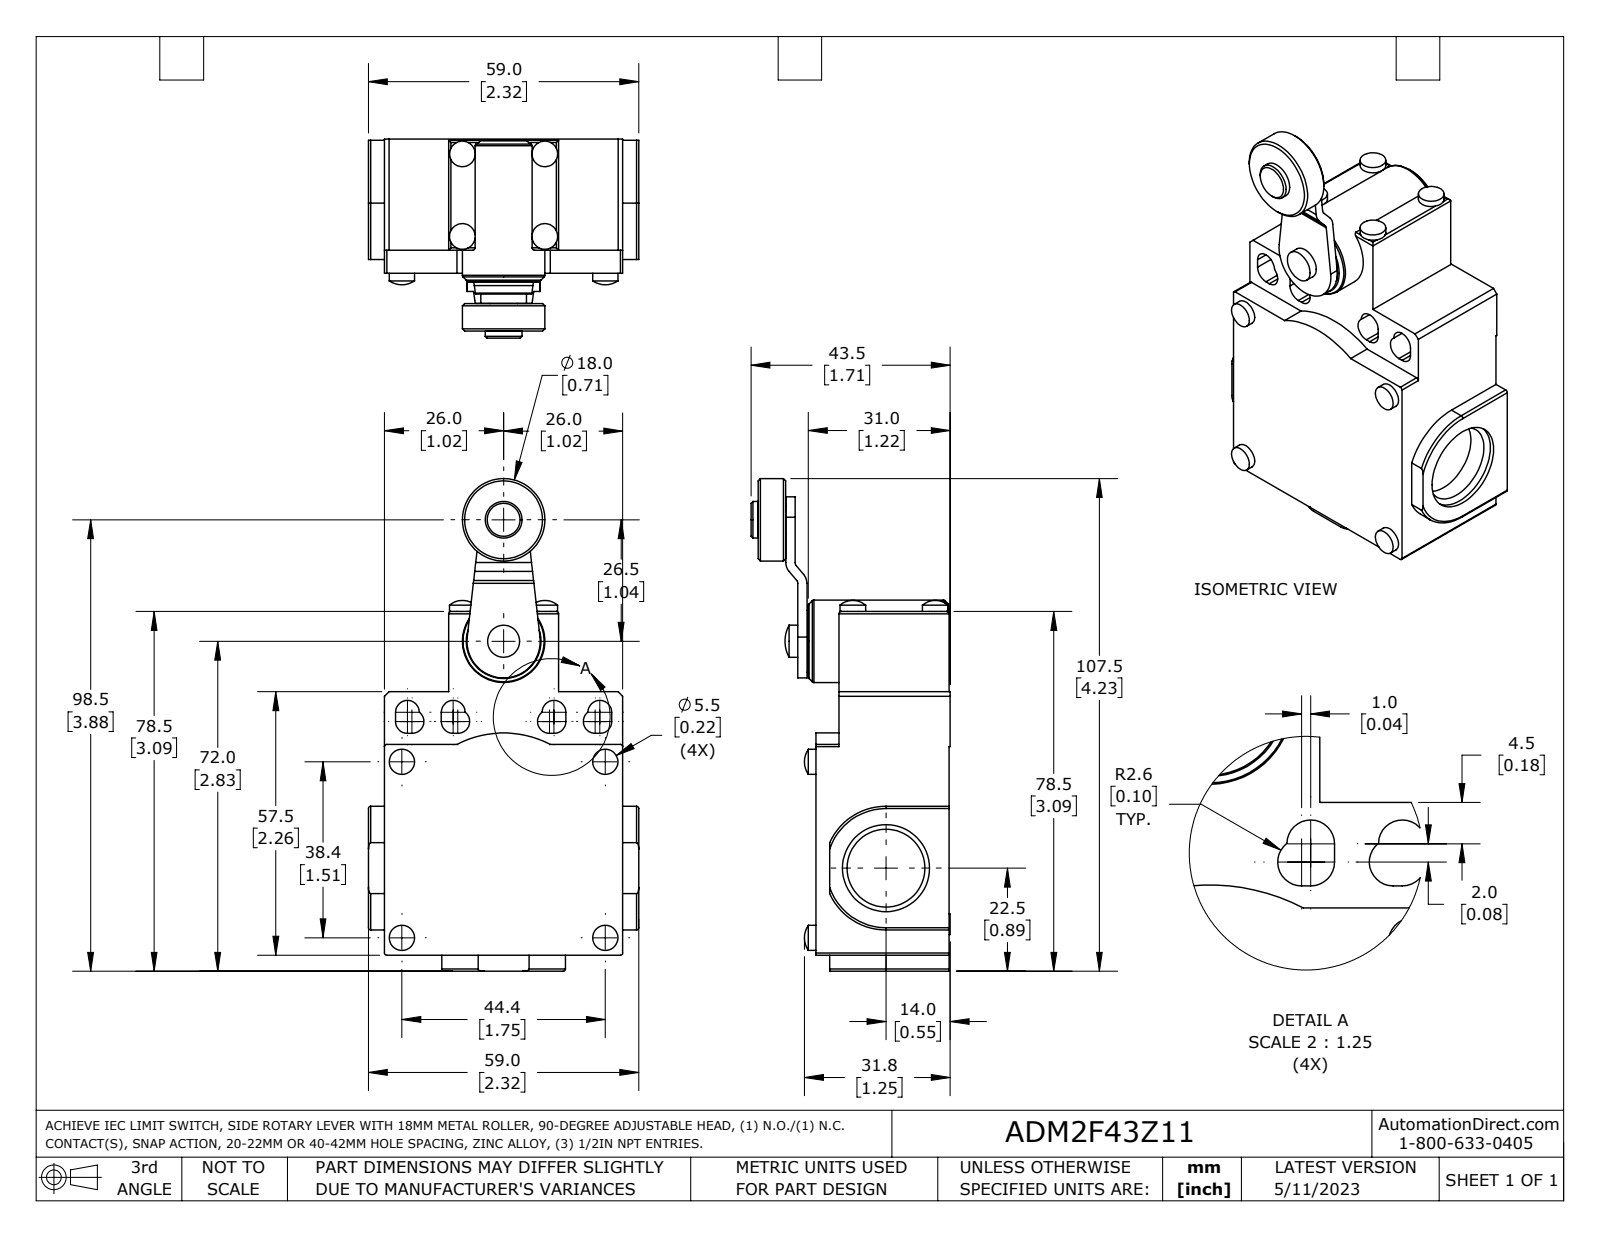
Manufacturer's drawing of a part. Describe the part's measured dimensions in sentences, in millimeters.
The part is named "ADM2F43Z11". Its 3-D file was written by "SolidWorks 2021 (AUTOMOTIVE_DESIGN)". It is 1 solid with 190 faces: 92 planar, 71 cylindrical and 27 other. Overall it measures 107.5 by 59 by 43.5 millimeters. Its volume is 98 550 cubic millimeters and its surface area 20 090 square millimeters. Round holes: 2 of diameter 17, 2 of diameter 19. Round bosses or shafts: 4 of diameter 5.6, 4 of diameter 5.5, 2 of diameter 18, 1 of diameter 14.9, 1 of diameter 13.5, 1 of diameter 8, 1 of diameter 7, 1 of diameter 6. Partial cylindrical surfaces (rounded edges, fillets, slot ends): 14 of radius 0.5, 12 of radius 2.6, 2 of radius 1, 2 of radius 3, 2 of radius 13.5, 1 of radius 5, 1 of radius 8, 1 of radius 10. The main face-to-face distances are 29.1, 3.5, 52, 24, 6, 17.5, 14, 38, 41.5, 2.5.
